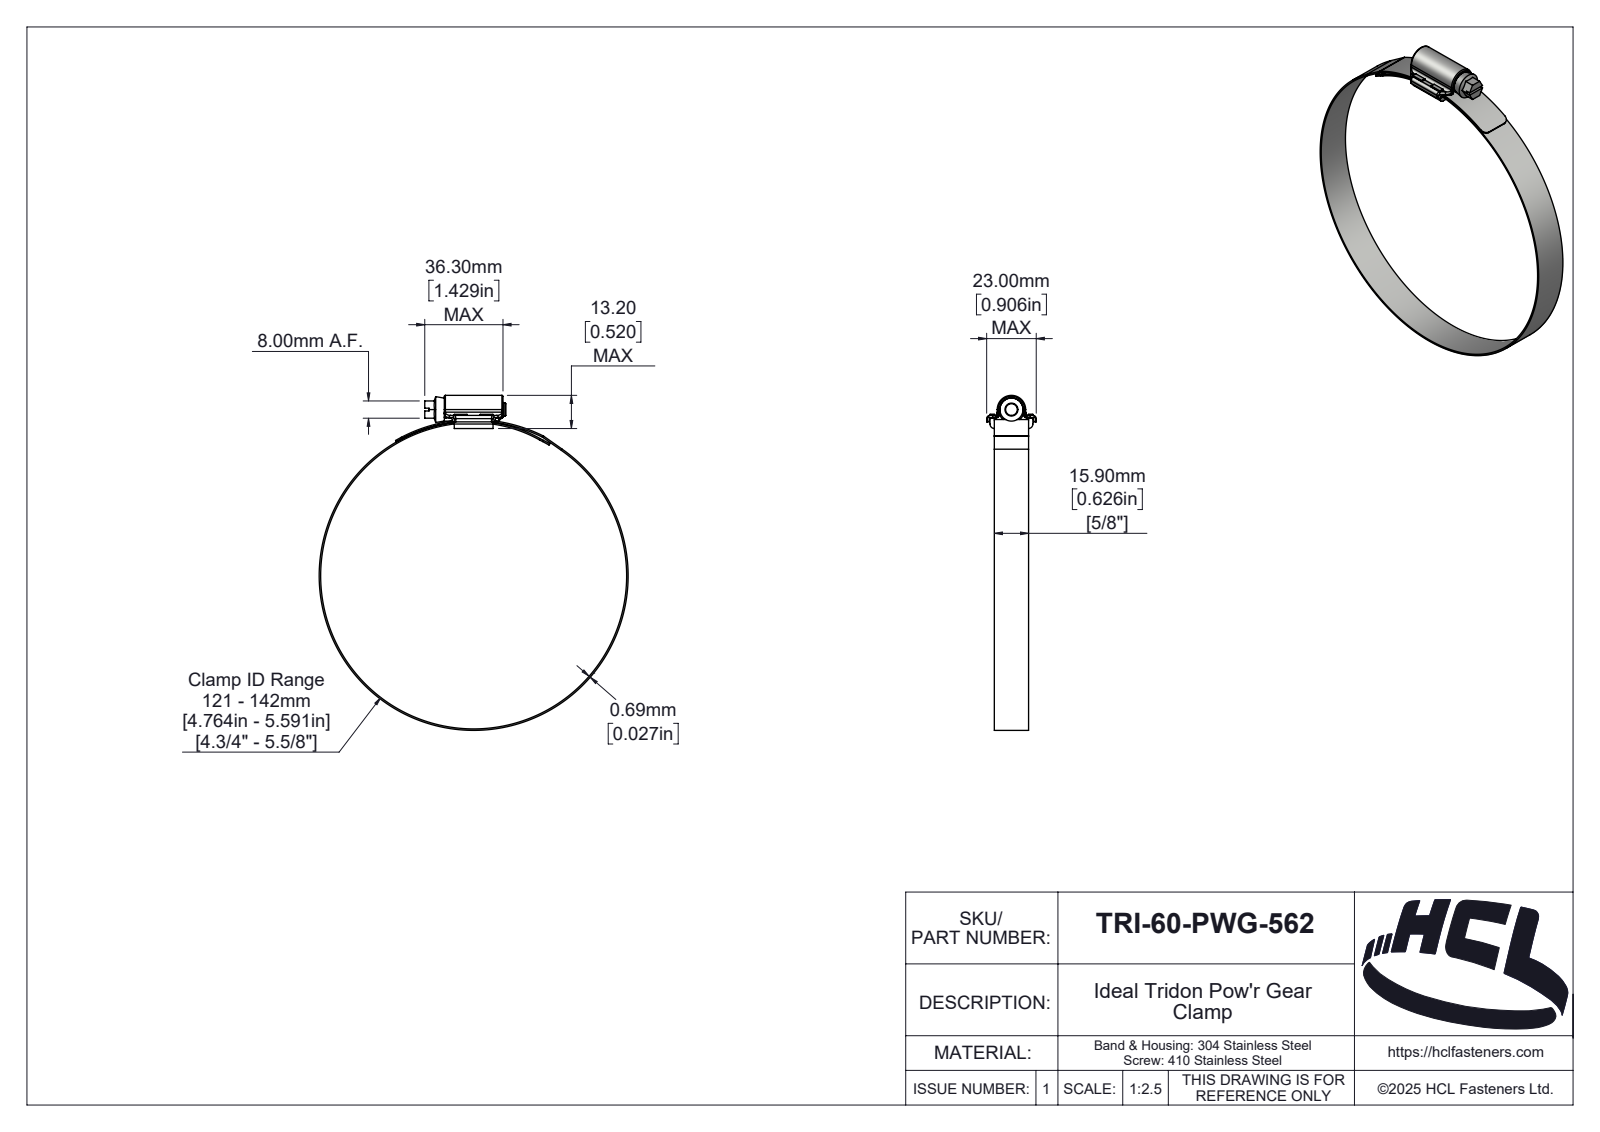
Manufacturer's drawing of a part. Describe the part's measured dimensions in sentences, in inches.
The part is named "TRI-60-PWG-562". Its 3-D file was written by "SolidWorks 2025 (AUTOMOTIVE_DESIGN)". It is 4 solids with 268 faces: 87 planar, 102 cylindrical and 79 other. Overall it measures 6.118 by 5.645 by 0.906 inches. Its volume is 0.667 cubic inches and its surface area 34.06 square inches. Round holes: 1 of diameter 5.591. Round bosses or shafts: 1 of diameter 5.645, 1 of diameter 0.421, 1 of diameter 0.236. Partial cylindrical surfaces (rounded edges, fillets, slot ends): 14 of radius 0.039, 4 of radius 0.02, 4 of radius 0.059, 3 of radius 0.079, 2 of radius 0.004, 2 of radius 0.083, 2 of radius 0.118, 1 of radius 0.018. The main face-to-face distances are 0.079, 0.626, 0.705, 0.027, 0.193, 0.047, 0.179, 0.132, 0.604, 0.1.
